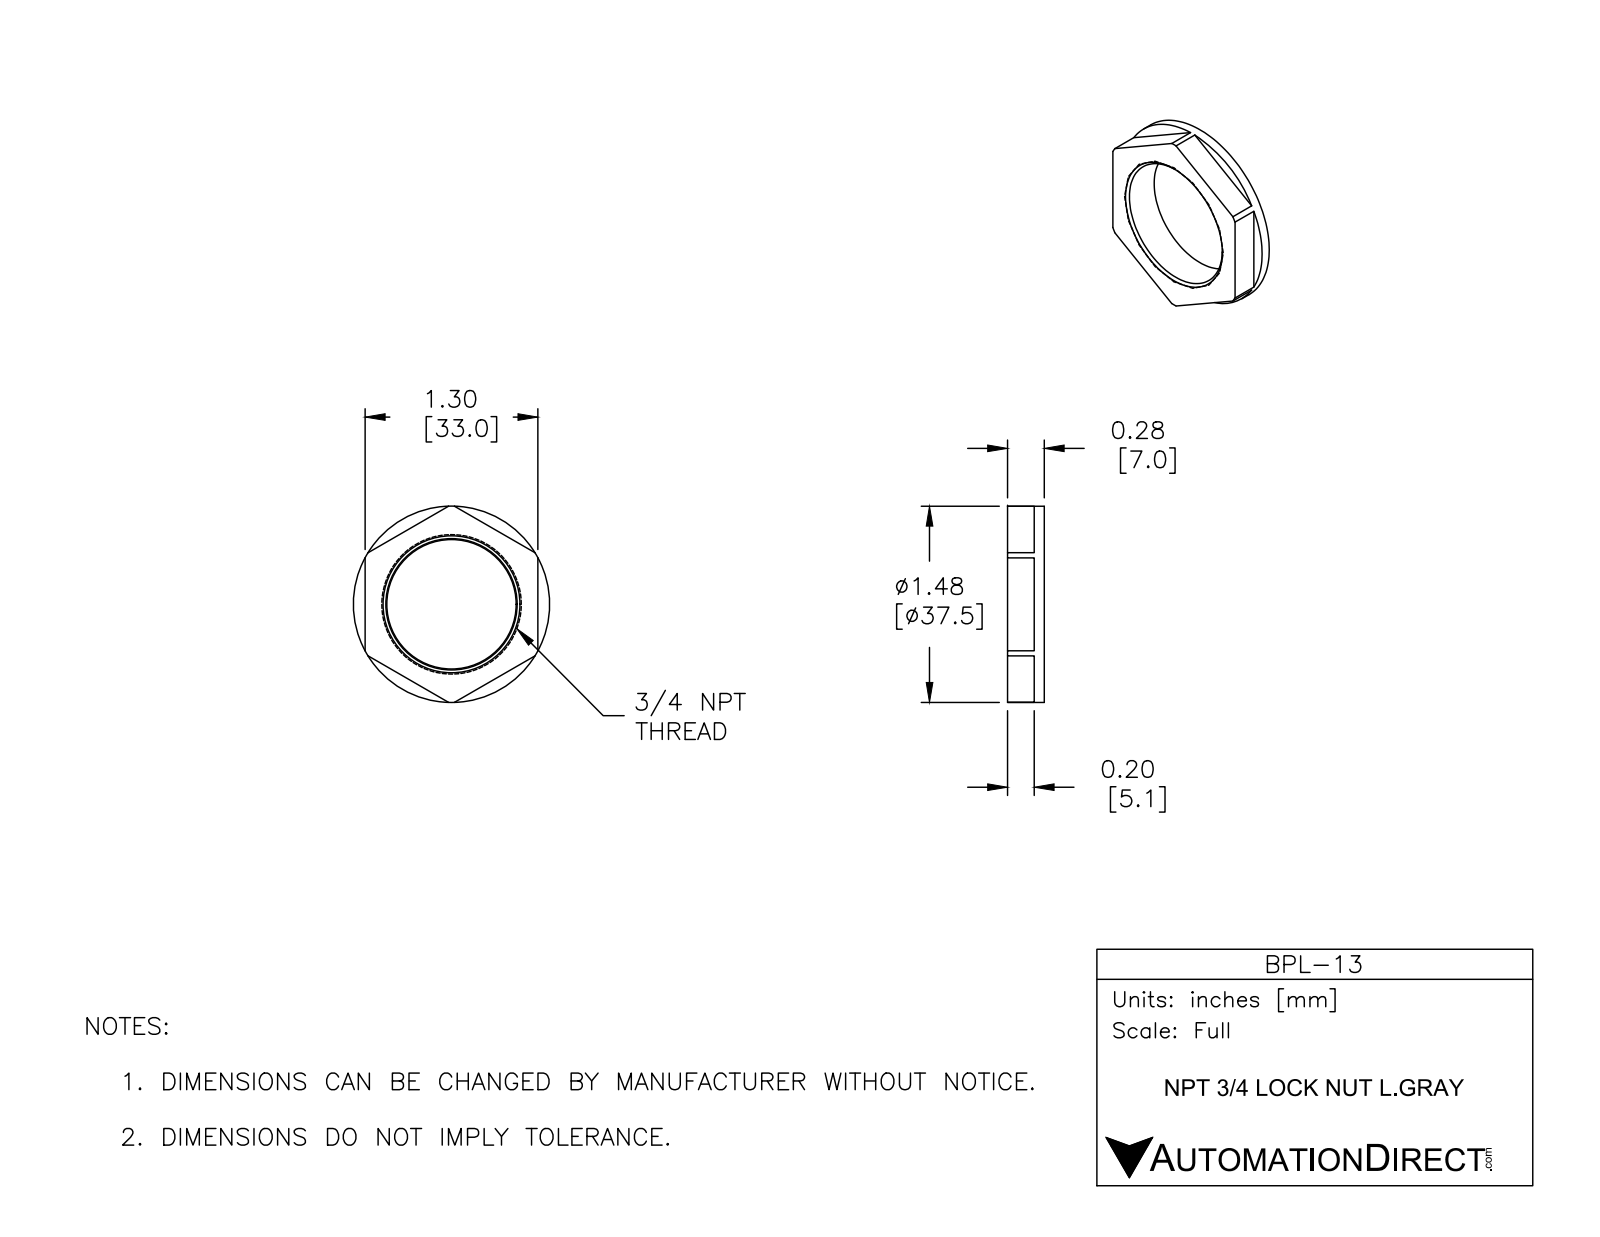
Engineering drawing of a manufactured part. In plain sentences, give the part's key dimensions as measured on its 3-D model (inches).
The part is named "BPL-13". Its 3-D file was written by "SolidWorks 2015 (CONFIG_CONTROL_DESIGN)". It is 1 solid with 20 faces: 14 planar, 2 cylindrical and 4 other. Overall it measures 1.476 by 1.476 by 0.276 inches. Its volume is 0.213 cubic inches and its surface area 3.969 square inches. Round bosses or shafts: 1 of diameter 1.476. The main face-to-face distances are 0.276, 1.3, 0.076, 0.2.
